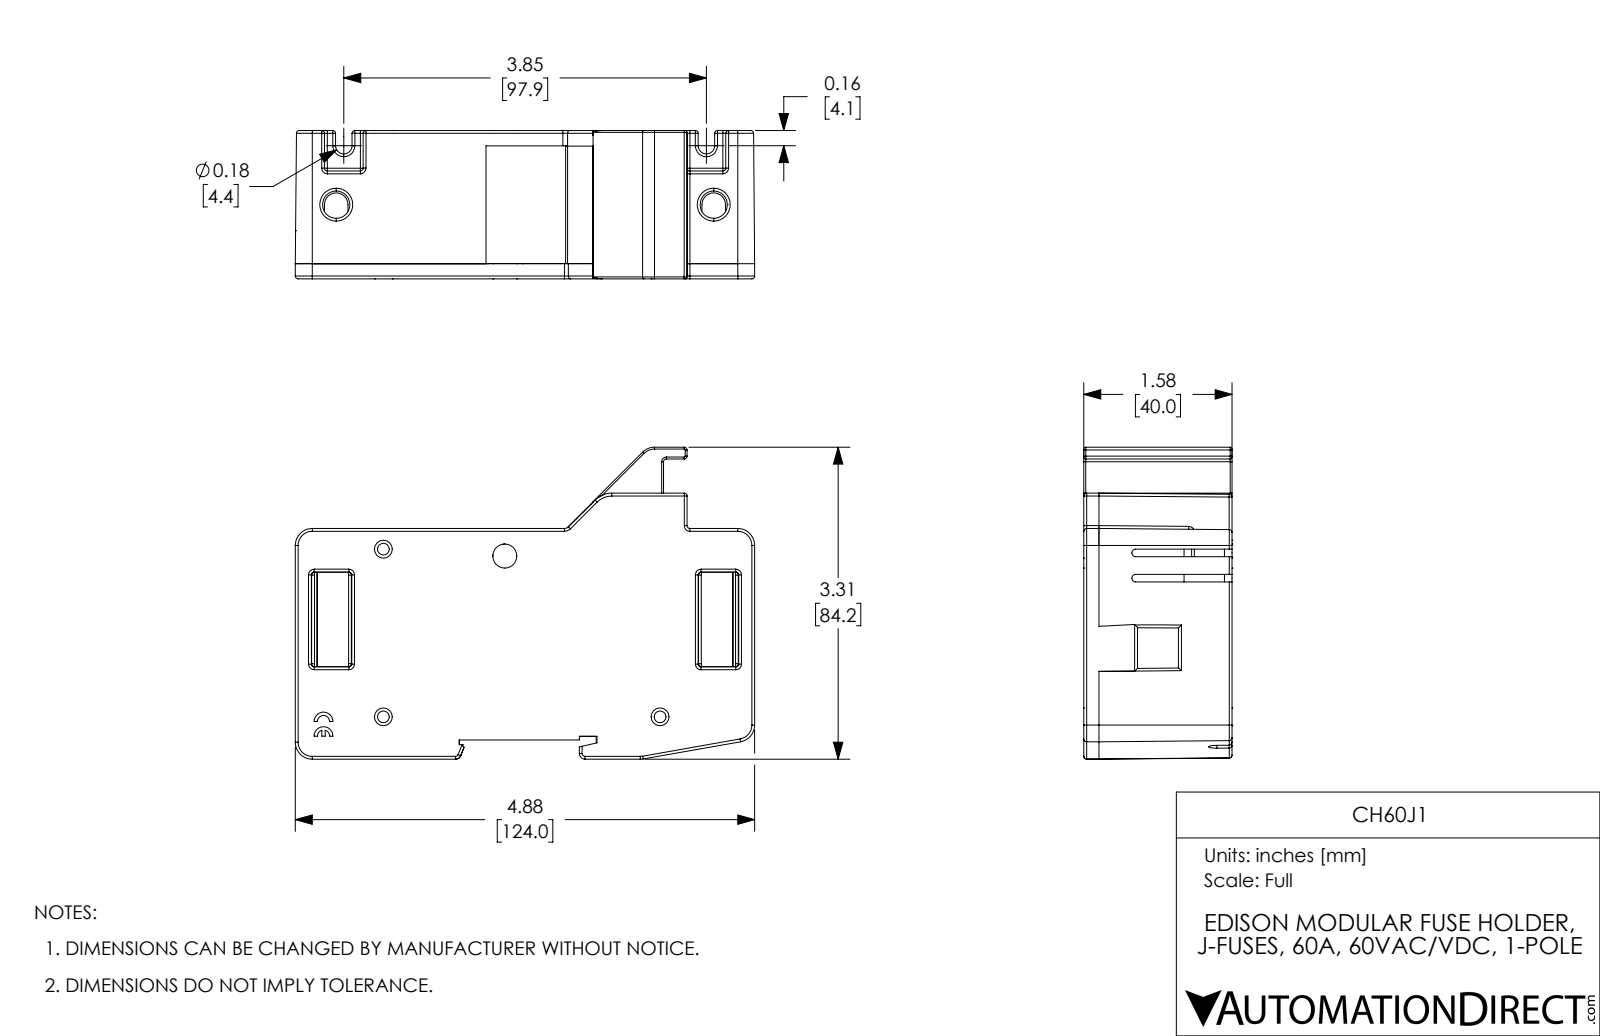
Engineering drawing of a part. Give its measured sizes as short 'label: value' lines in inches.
name: CH60J1
written by: SolidWorks 2017 (AUTOMOTIVE_DESIGN)
unit: in
bodies: 3 solids, 301 faces (82 planar, 150 cylindrical, 69 other)
size: 4.881 × 3.313 × 1.575
volume: 17.11 in³; area: 67.57 in²
holes: 3× ⌀0.125, 3× ⌀0.19, 1× ⌀0.255
rounds: 71× R0.03, 10× R0.02, 6× R0.04, 6× R0.18, 4× R0.06, 1× R0.087, 1× R0.088, 1× R0.25
face distances: 1.575, 2.45, 4.881, 0.125, 0.43, 2.325, 0.204, 2.121, 2.246, 0.03
hole spacings: 1.292, 1.78, 2.139, 2.374, 2.94, 3.437
